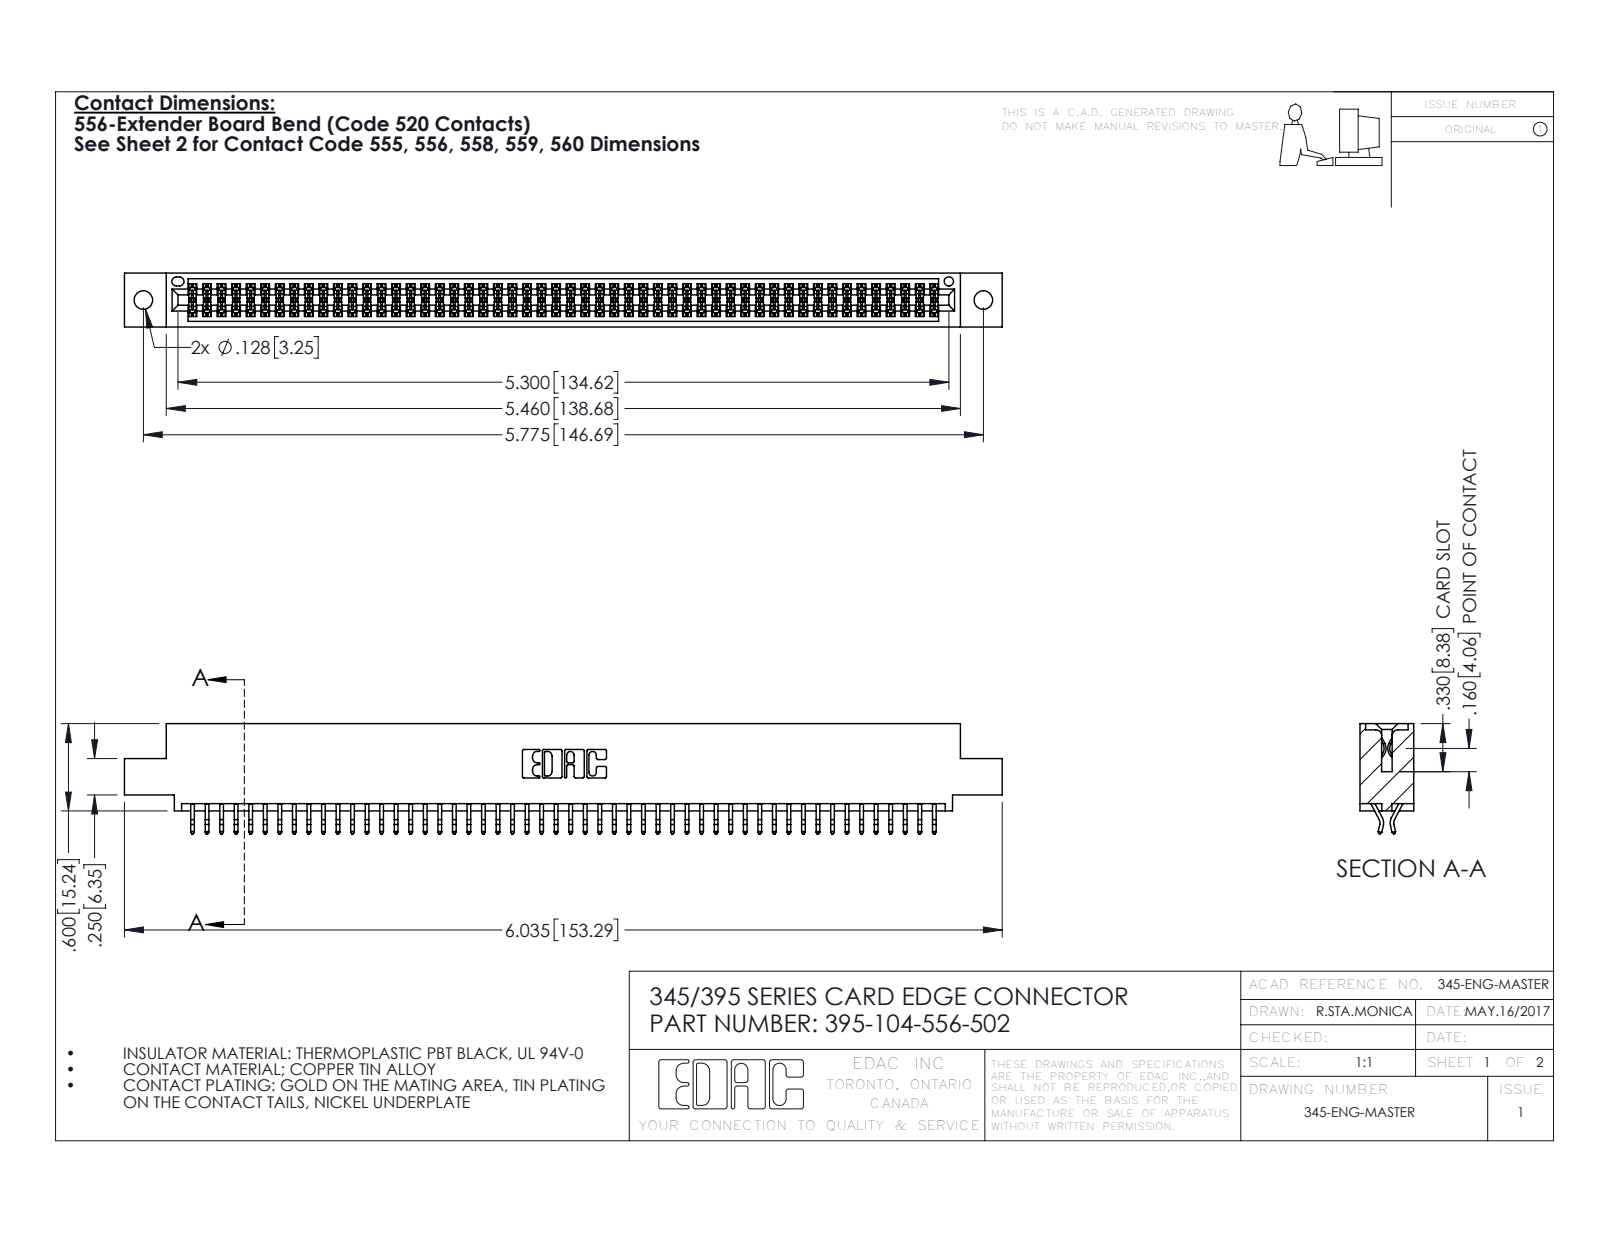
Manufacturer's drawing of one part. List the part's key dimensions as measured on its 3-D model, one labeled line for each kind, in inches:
Part name (STEP PRODUCT): 345 Part_0.110 Offset - 0.128 Dia; 395-104-556-502; 345-292-001_556 Tail
STEP written by: SolidWorks 2016 (CONFIG_CONTROL_DESIGN)
Units: inches
Bodies: 105 solids, 5954 faces (3932 planar, 2022 cylindrical, 0 other)
Overall size (bounding box): 6.035 × 0.757 × 0.37
Volume: 0.907 in³ · Surface area: 33.95 in²
Round holes (diameter × count): ⌀0.128 ×2, ⌀0.064 ×1
Partial cylindrical surfaces — rounded edges, fillets, slot ends (radius × count): R0.006 ×156, R0.01 ×22, R0.007 ×6, R0.031 ×6, R0.026 ×3, R0.01 ×2, R0.014 ×2, R0.019 ×2
Main face-to-face distances: 0.298, 0.072, 0.37, 0.2, 0.025, 0.098, 0.272, 0.225, 0.175, 0.149
Hole centre spacings: 0.27, 5.539, 5.775
